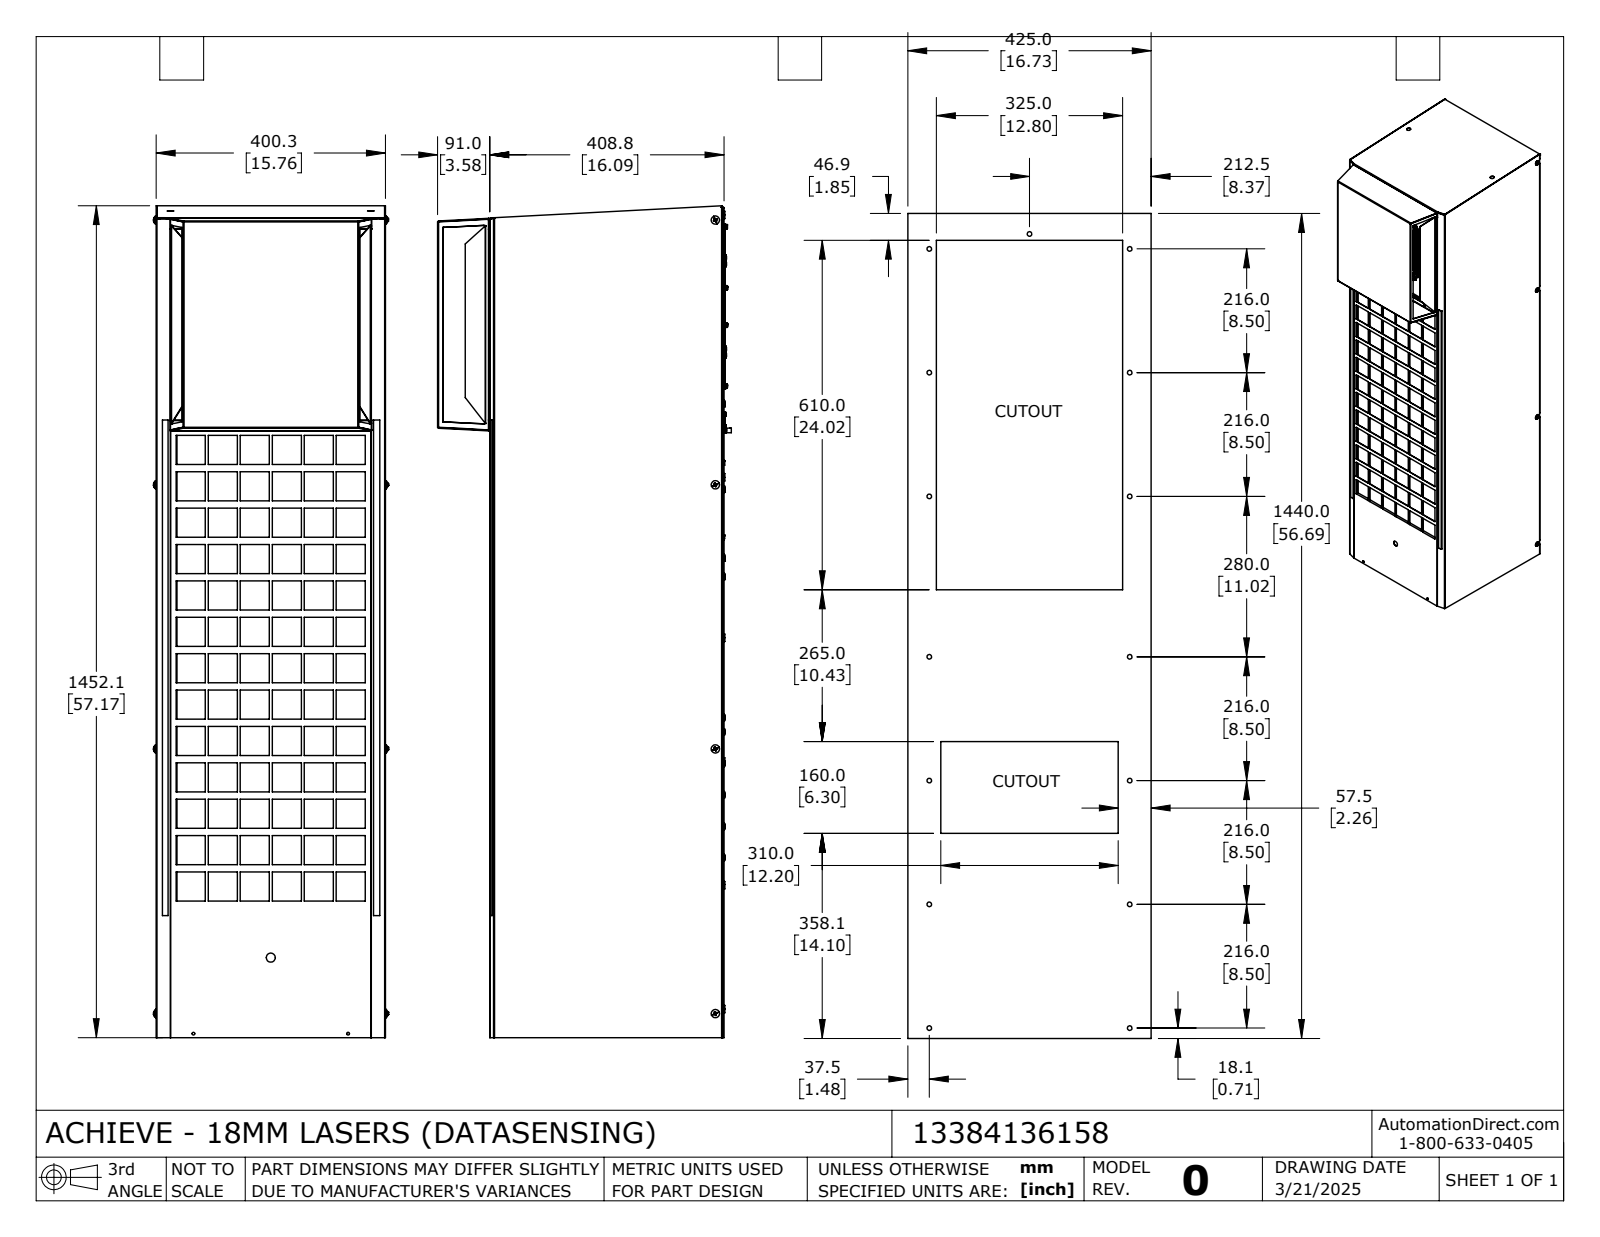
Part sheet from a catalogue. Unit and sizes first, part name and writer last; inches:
Units: inches
Overall size (bounding box): 57.171 × 20.19 × 16.113
Round holes (diameter × count): ⌀0.107 ×48, ⌀0.165 ×47, ⌀0.283 ×18, ⌀0.189 ×14, ⌀0.098 ×4, ⌀0.161 ×4, ⌀0.374 ×4, ⌀0.125 ×2, ⌀0.276 ×2, ⌀0.472 ×2, ⌀0.945 ×2, ⌀0.122 ×1
Round bosses / shafts (diameter × count): ⌀0.178 ×35, ⌀0.512 ×18, ⌀0.315 ×12, ⌀0.157 ×12, ⌀0.122 ×12, ⌀0.354 ×6, ⌀0.079 ×5, ⌀0.573 ×4
Partial cylindrical surfaces — rounded edges, fillets, slot ends (radius × count): R0.125 ×352, R0.031 ×43, R0.076 ×28, R0.198 ×18, R0.087 ×13, R0.132 ×6, R0.083 ×5, R0.118 ×5
Main face-to-face distances: 0.045, 0.045, 0.056, 15.714, 15.759, 15.669, 15.715, 0.28, 0.235, 15.435
Hole centre spacings: 7.48, 14.961, 22.441, 3.028, 0.022, 0.037, 7.874, 29.921
Volume: 13 374 in³ · Surface area: 11 995 in²
Bodies: 1 solid, 6463 faces (3532 planar, 1827 cylindrical, 1104 other)
Part name (STEP PRODUCT): 13384136158_Default
STEP written by: SolidWorks 2024 (CONFIG_CONTROL_DESIGN)
